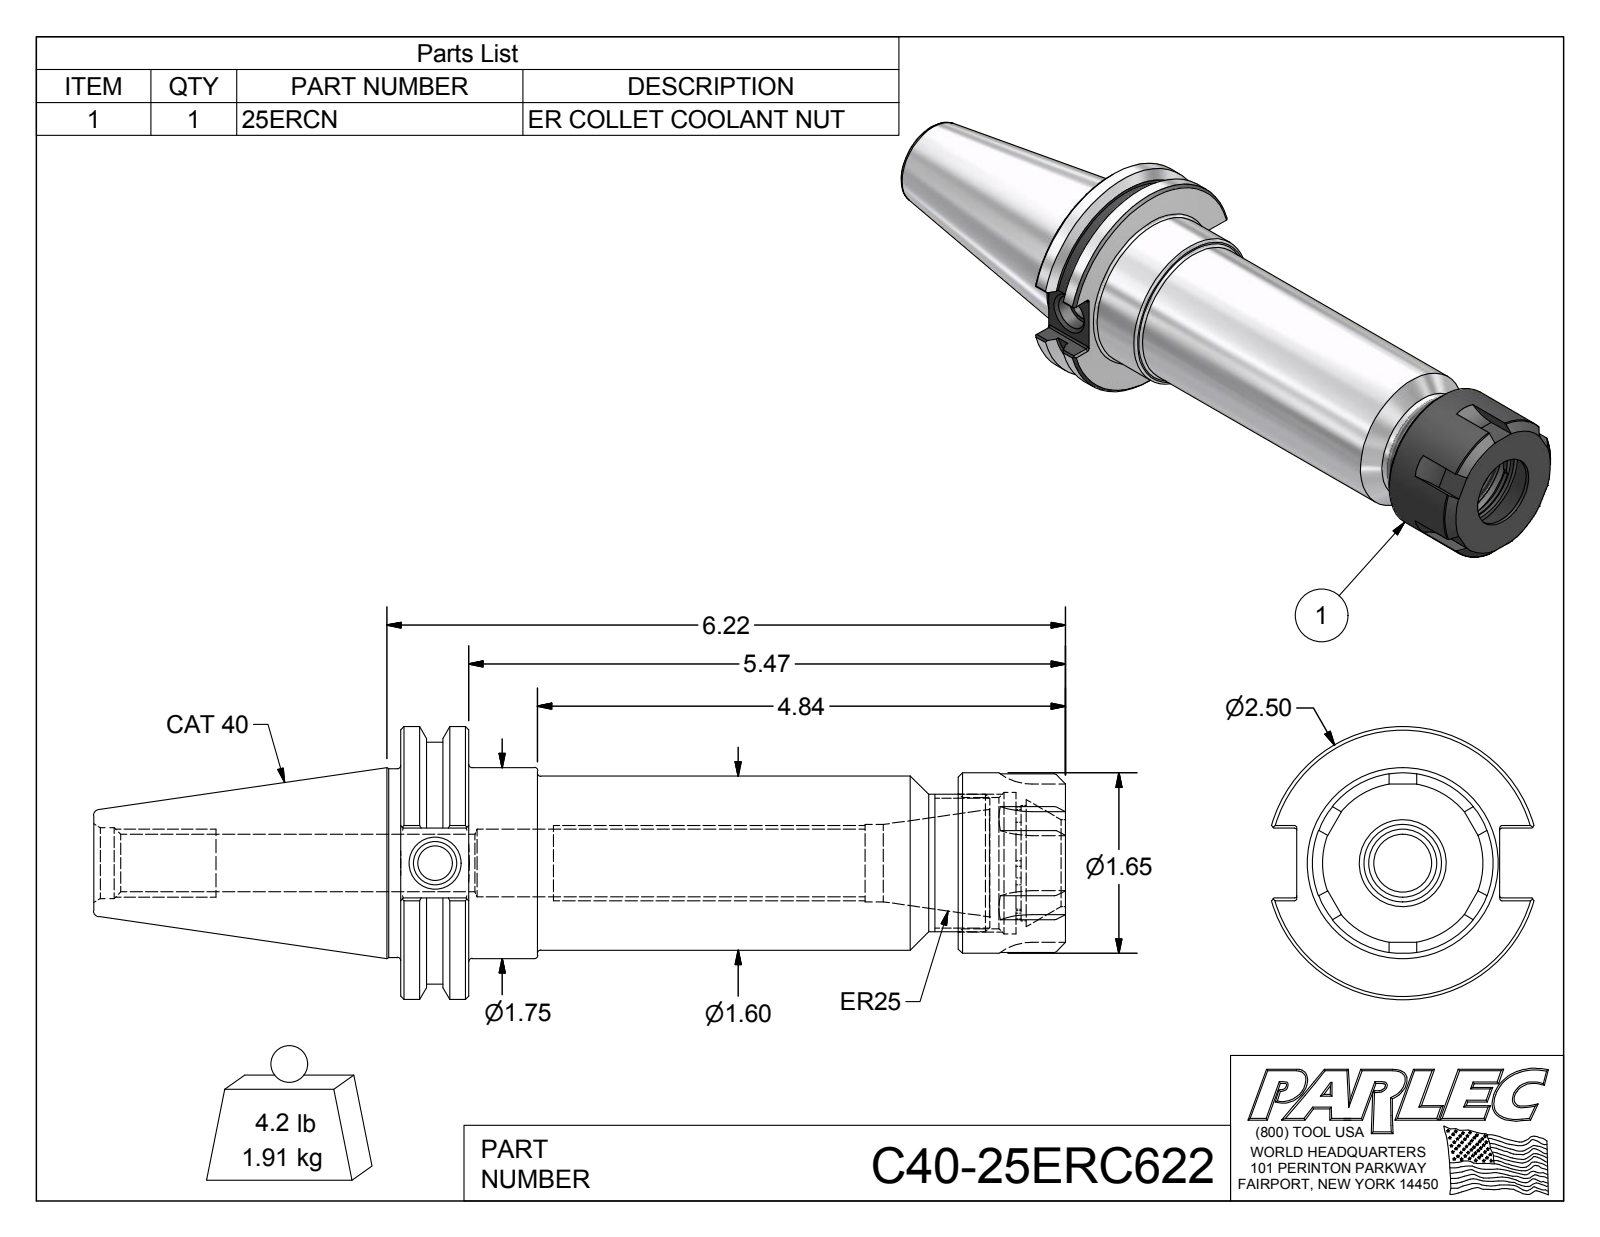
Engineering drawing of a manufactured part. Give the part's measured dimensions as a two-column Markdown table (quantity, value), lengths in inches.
| quantity | value |
| --- | --- |
| part name | C40-25ERC622; C40-25ER6-1; 25ERCN |
| STEP written by | Autodesk Inventor 2012 (AUTOMOTIVE_DESIGN) |
| units | inches |
| bodies | 2 solids, 145 faces (61 planar, 44 cylindrical, 40 other) |
| overall size | 8.908 × 2.5 × 2.403 |
| volume | 14.77 in³ |
| surface area | 75.92 in² |
| round holes (diameter × count) | 0.315 × 1, 0.399 × 1, 0.527 × 1, 0.62 × 1, 0.648 × 1, 0.71 × 1, 0.794 × 1, 1.057 × 1, 1.201 × 1, 1.294 × 1 |
| round bosses / shafts (diameter × count) | 2.5 × 1, 2.219 × 1, 1.75 × 1, 1.73 × 1, 1.654 × 1, 1.595 × 1, 1.26 × 1 |
| partial cylindrical surfaces (radius × count) | 0.02 × 12, 0.5 × 6, 0.472 × 1, 0.515 × 1 |
| main face-to-face distances | 0.625, 6.095, 5.47, 5.111, 4.486, 0.984, 5.642, 5.017, 0.531, 0.453 |
